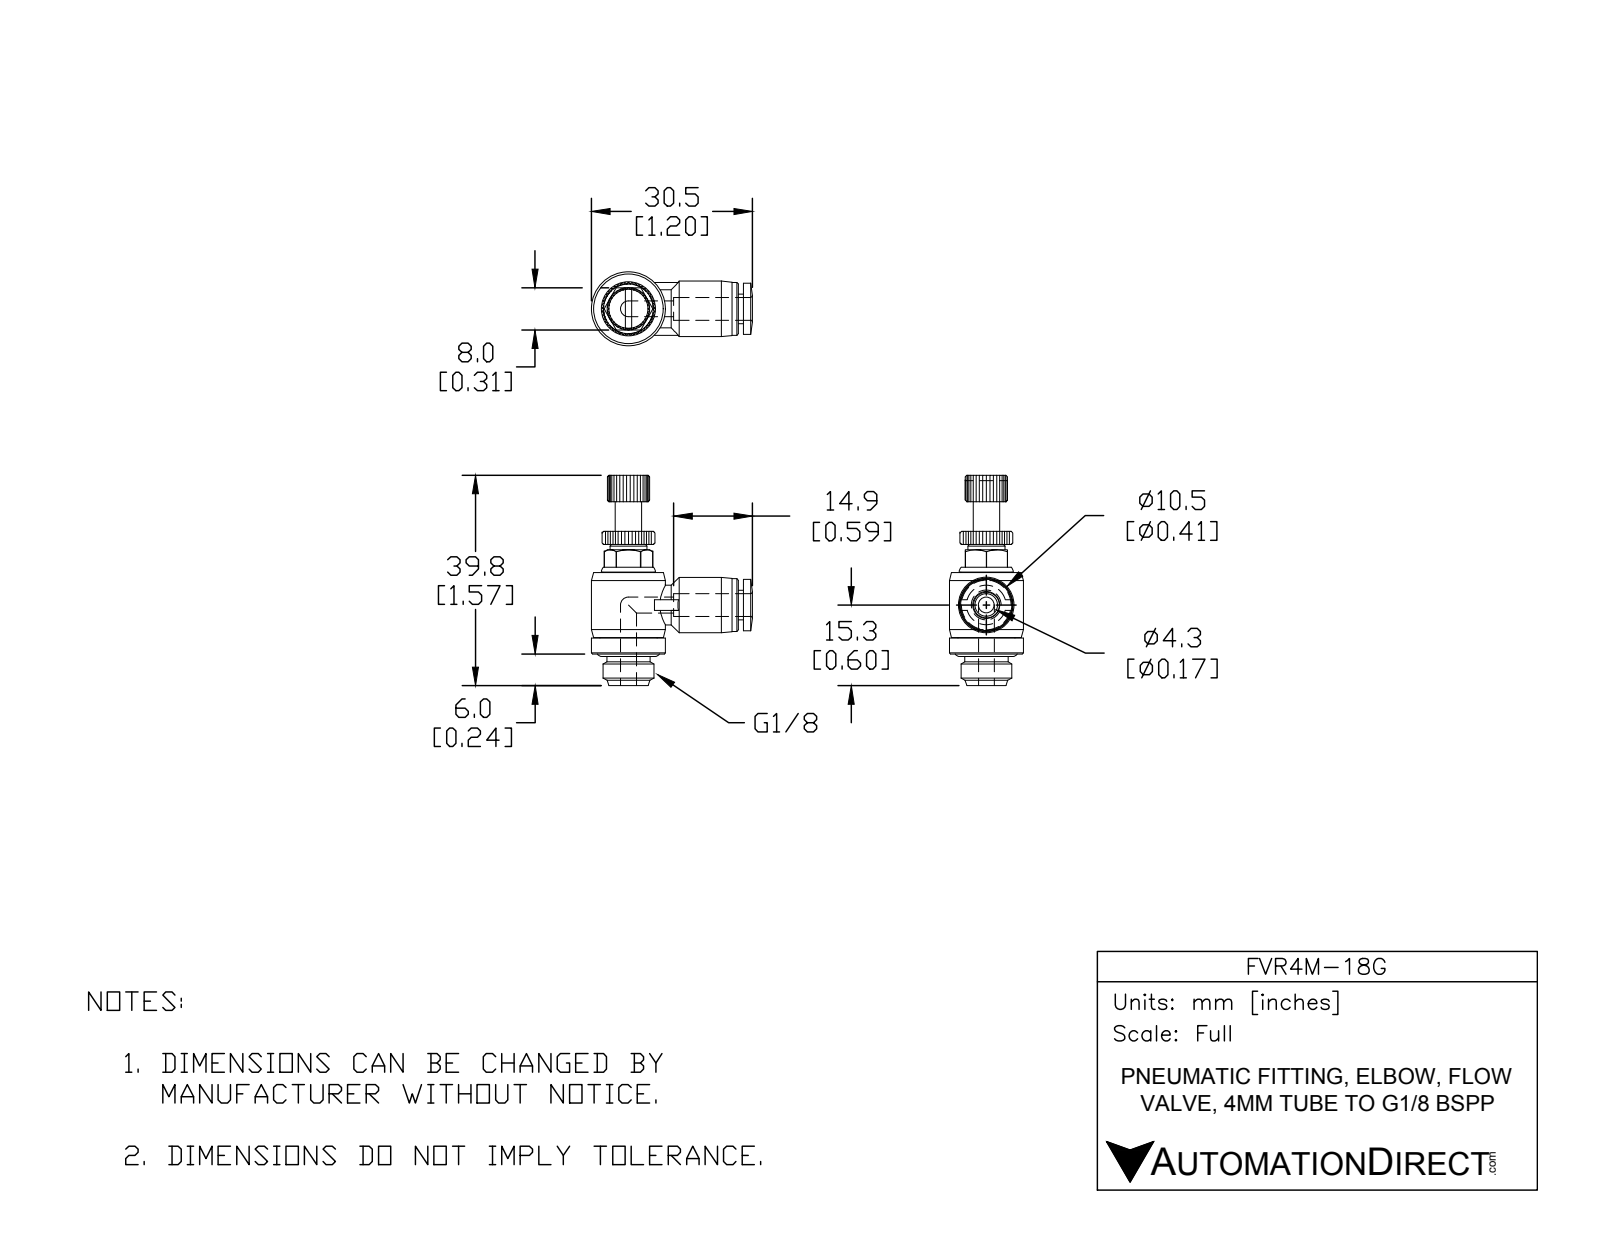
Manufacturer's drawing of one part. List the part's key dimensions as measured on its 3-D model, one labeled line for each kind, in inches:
Part name (STEP PRODUCT): FVR4M-18G
STEP written by: SolidWorks 2015 (AUTOMOTIVE_DESIGN)
Units: inches
Bodies: 2 solids, 511 faces (192 planar, 121 cylindrical, 198 other)
Overall size (bounding box): 1.567 × 1.199 × 0.551
Volume: 0.269 in³ · Surface area: 4.991 in²
Round holes (diameter × count): ⌀0.118 ×2, ⌀0.169 ×1
Round bosses / shafts (diameter × count): ⌀0.382 ×2, ⌀0.551 ×1, ⌀0.425 ×1, ⌀0.413 ×1, ⌀0.394 ×1, ⌀0.378 ×1, ⌀0.323 ×1, ⌀0.295 ×1
Partial cylindrical surfaces — rounded edges, fillets, slot ends (radius × count): R0.157 ×1, R0.181 ×1, R0.197 ×1
Main face-to-face distances: 0.488, 0.795, 0.206, 0.354, 0.039, 0.307, 0.358, 0.067, 0.063, 0.551
